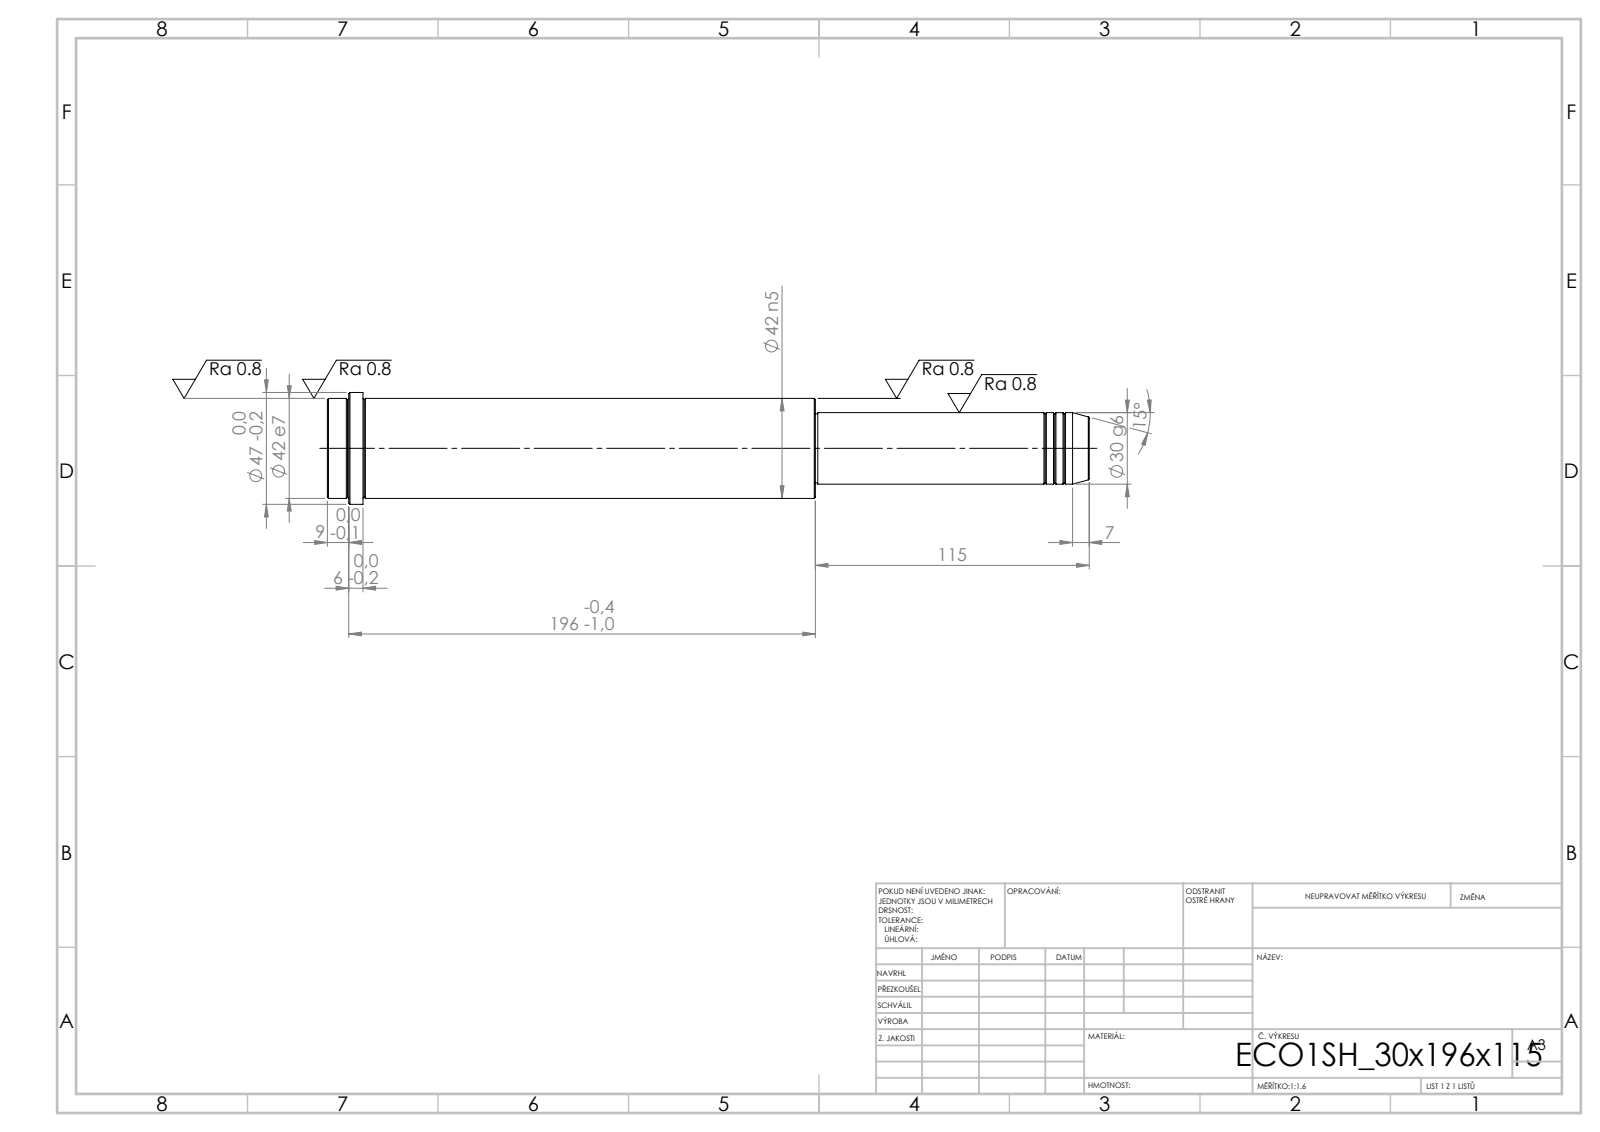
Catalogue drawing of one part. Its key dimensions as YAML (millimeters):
step_written_by: "SolidWorks 2019 (CONFIG_CONTROL_DESIGN)"
units: millimeters
bodies: {solids: 1, faces: 52, planar: 6, cylindrical: 16, other: 30}
overall_size: [320, 47, 47]
volume: 366497
surface_area: 41522
round_bosses_or_shafts:
  - {diameter: 47, count: 1}
  - {diameter: 42, count: 1}
  - {diameter: 30, count: 1}
  - {diameter: 29, count: 1}
face_to_face_distances: [205, 115, 320, 305, 190, 15, 311, 196, 6, 9]
